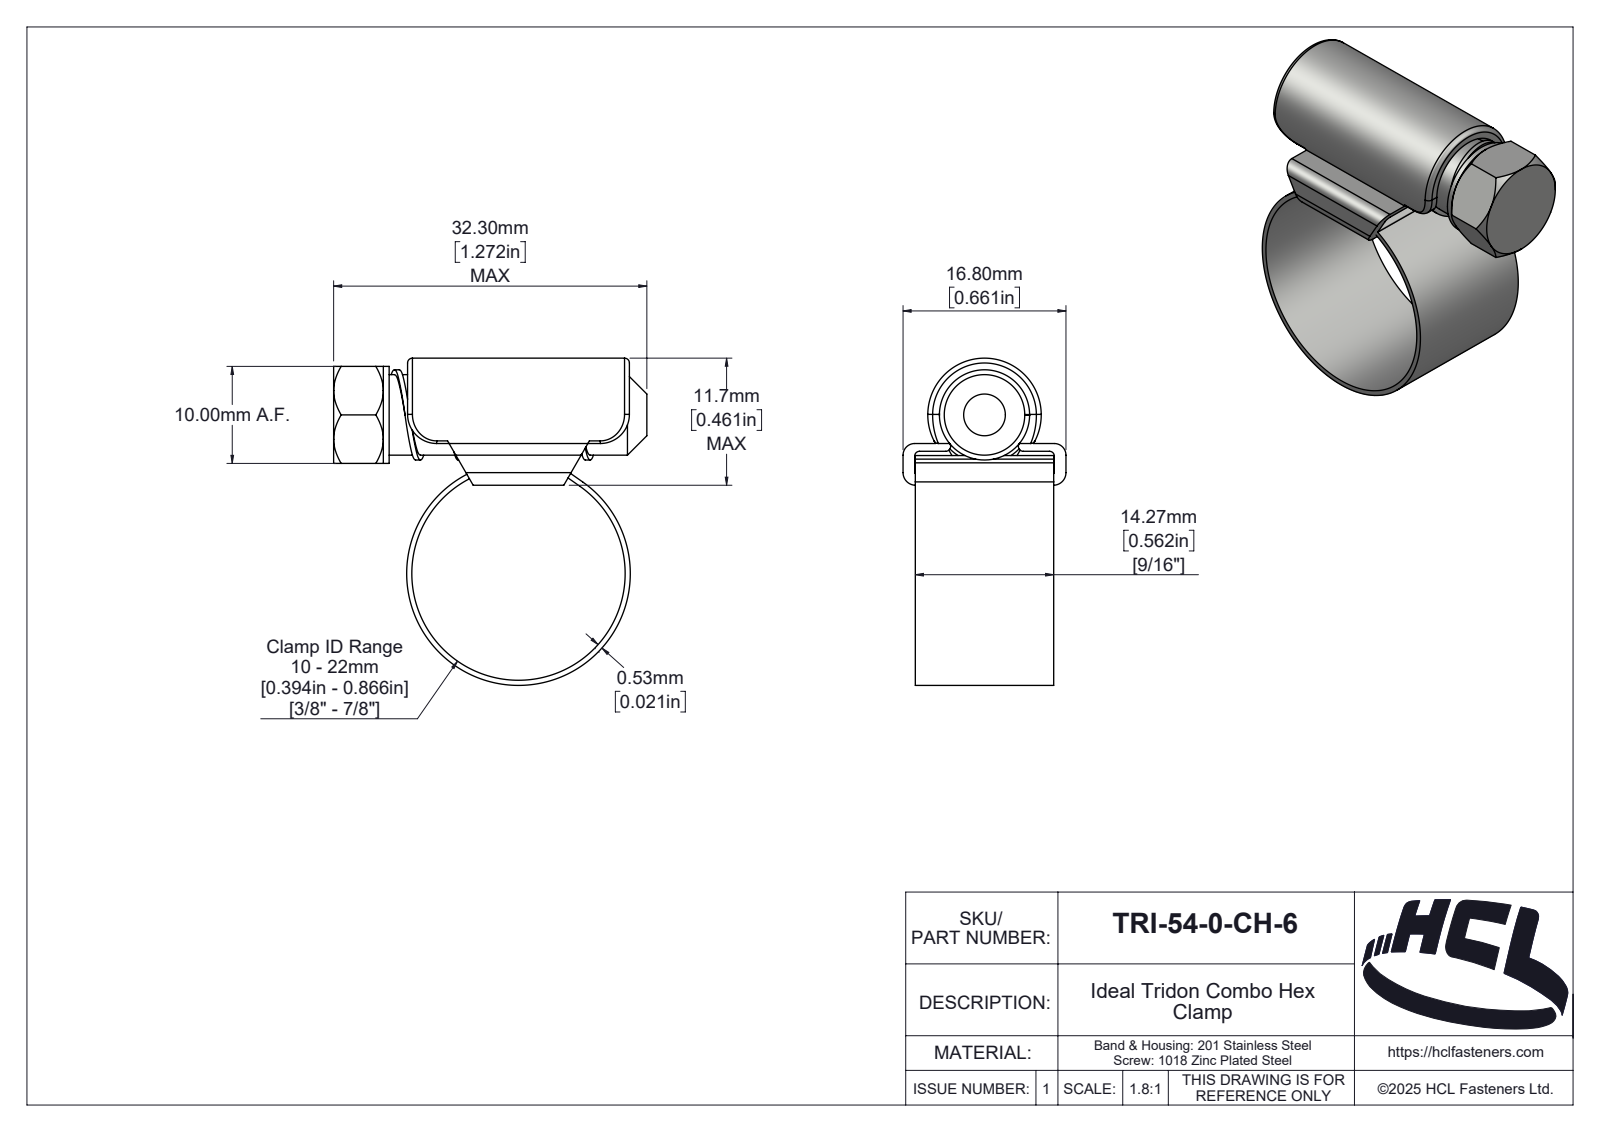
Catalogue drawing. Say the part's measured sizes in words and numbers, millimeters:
The part is named "TRI-54-0-CH-6". Its 3-D file was written by "SolidWorks 2025 (AUTOMOTIVE_DESIGN)". It is 3 solids with 212 faces: 35 planar, 101 cylindrical and 76 other. Overall it measures 33.73 by 32.3 by 16.8 millimeters. Its volume is 3 454 cubic millimeters and its surface area 5 210 square millimeters. Round holes: 1 of diameter 22. Round bosses or shafts: 1 of diameter 23.06, 1 of diameter 10, 1 of diameter 8.3. Partial cylindrical surfaces (rounded edges, fillets, slot ends): 6 of radius 0.5, 4 of radius 3, 2 of radius 0.1, 2 of radius 1.2, 2 of radius 1.3, 1 of radius 0.46, 1 of radius 1.89, 1 of radius 2. The main face-to-face distances are 1.2, 3.5, 2.3, 4.3, 3.1, 0.8, 9.99, 0.53, 1.27, 15.53.
